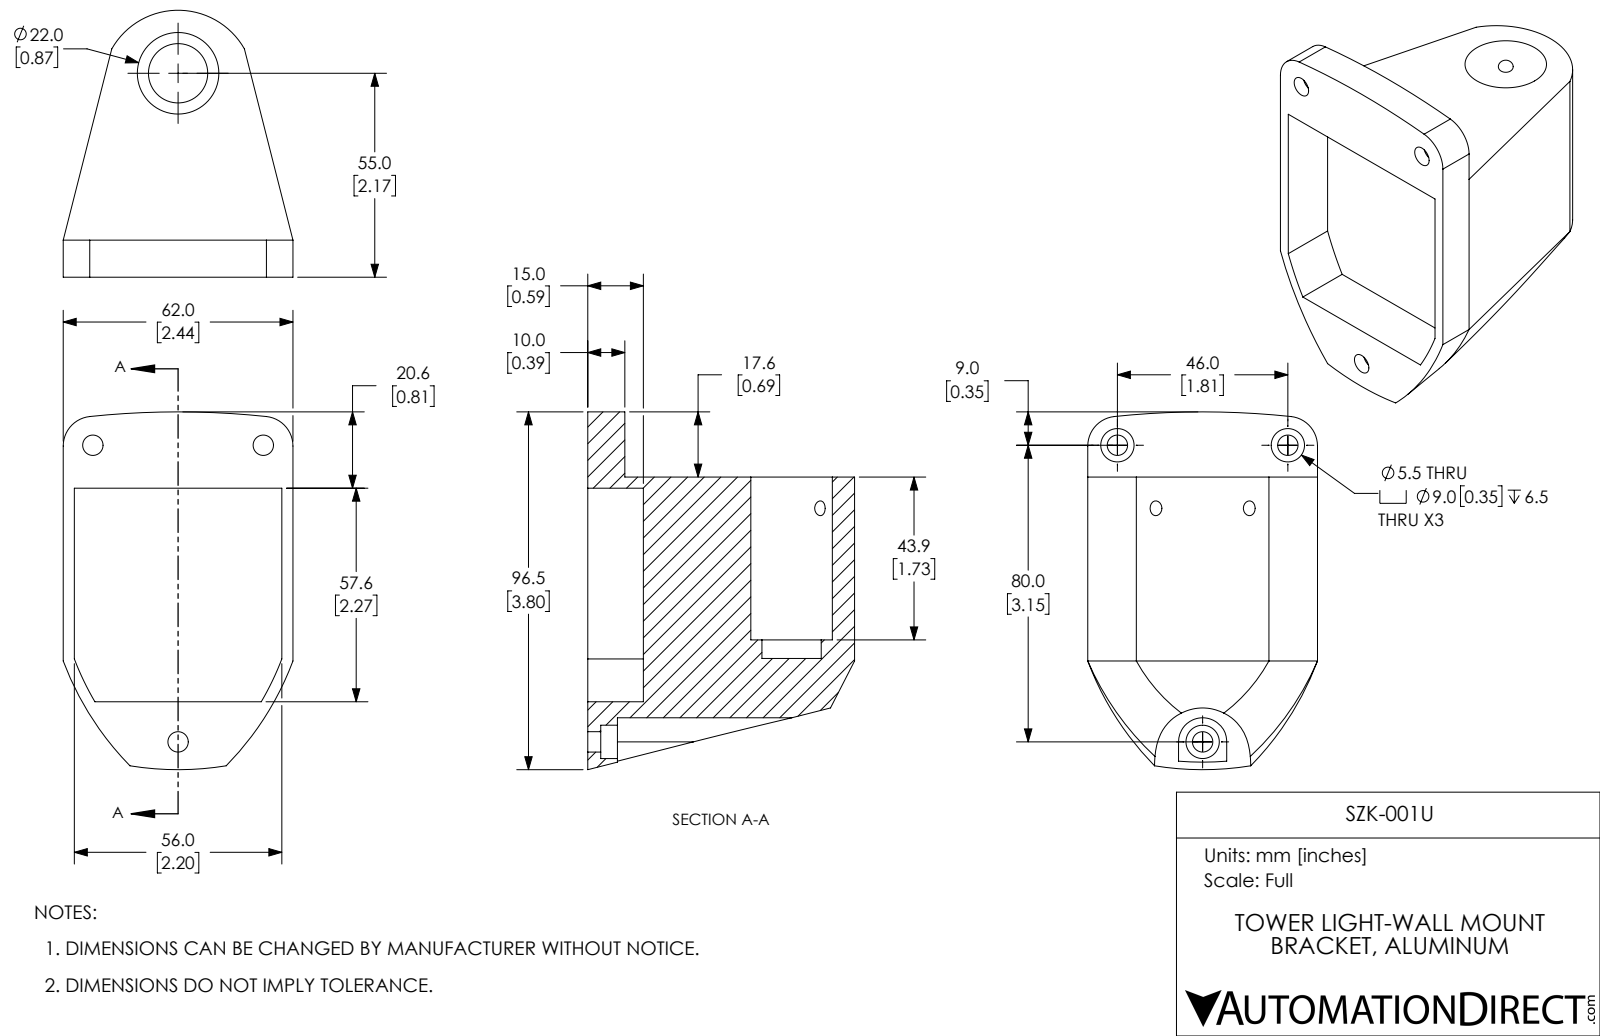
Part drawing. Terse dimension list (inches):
name: SZK-001U
written by: SolidWorks 2017 (AUTOMOTIVE_DESIGN)
unit: in
bodies: 1 solid, 53 faces (20 planar, 27 cylindrical, 6 other)
size: 3.799 × 2.835 × 2.441
volume: 9.95 in³; area: 48.56 in²
holes: 3× ⌀0.217, 3× ⌀0.354, 2× ⌀0.157, 1× ⌀0.63, 1× ⌀0.866
rounds: 2× R0.315, 2× R3.07, 1× R0.256, 1× R0.81, 1× R8.937
face distances: 0.591, 0.118, 2.323, 0.197, 0.394, 2.205, 2.268, 2.386, 2.441, 0.46
hole spacings: 3.277, 1.811
